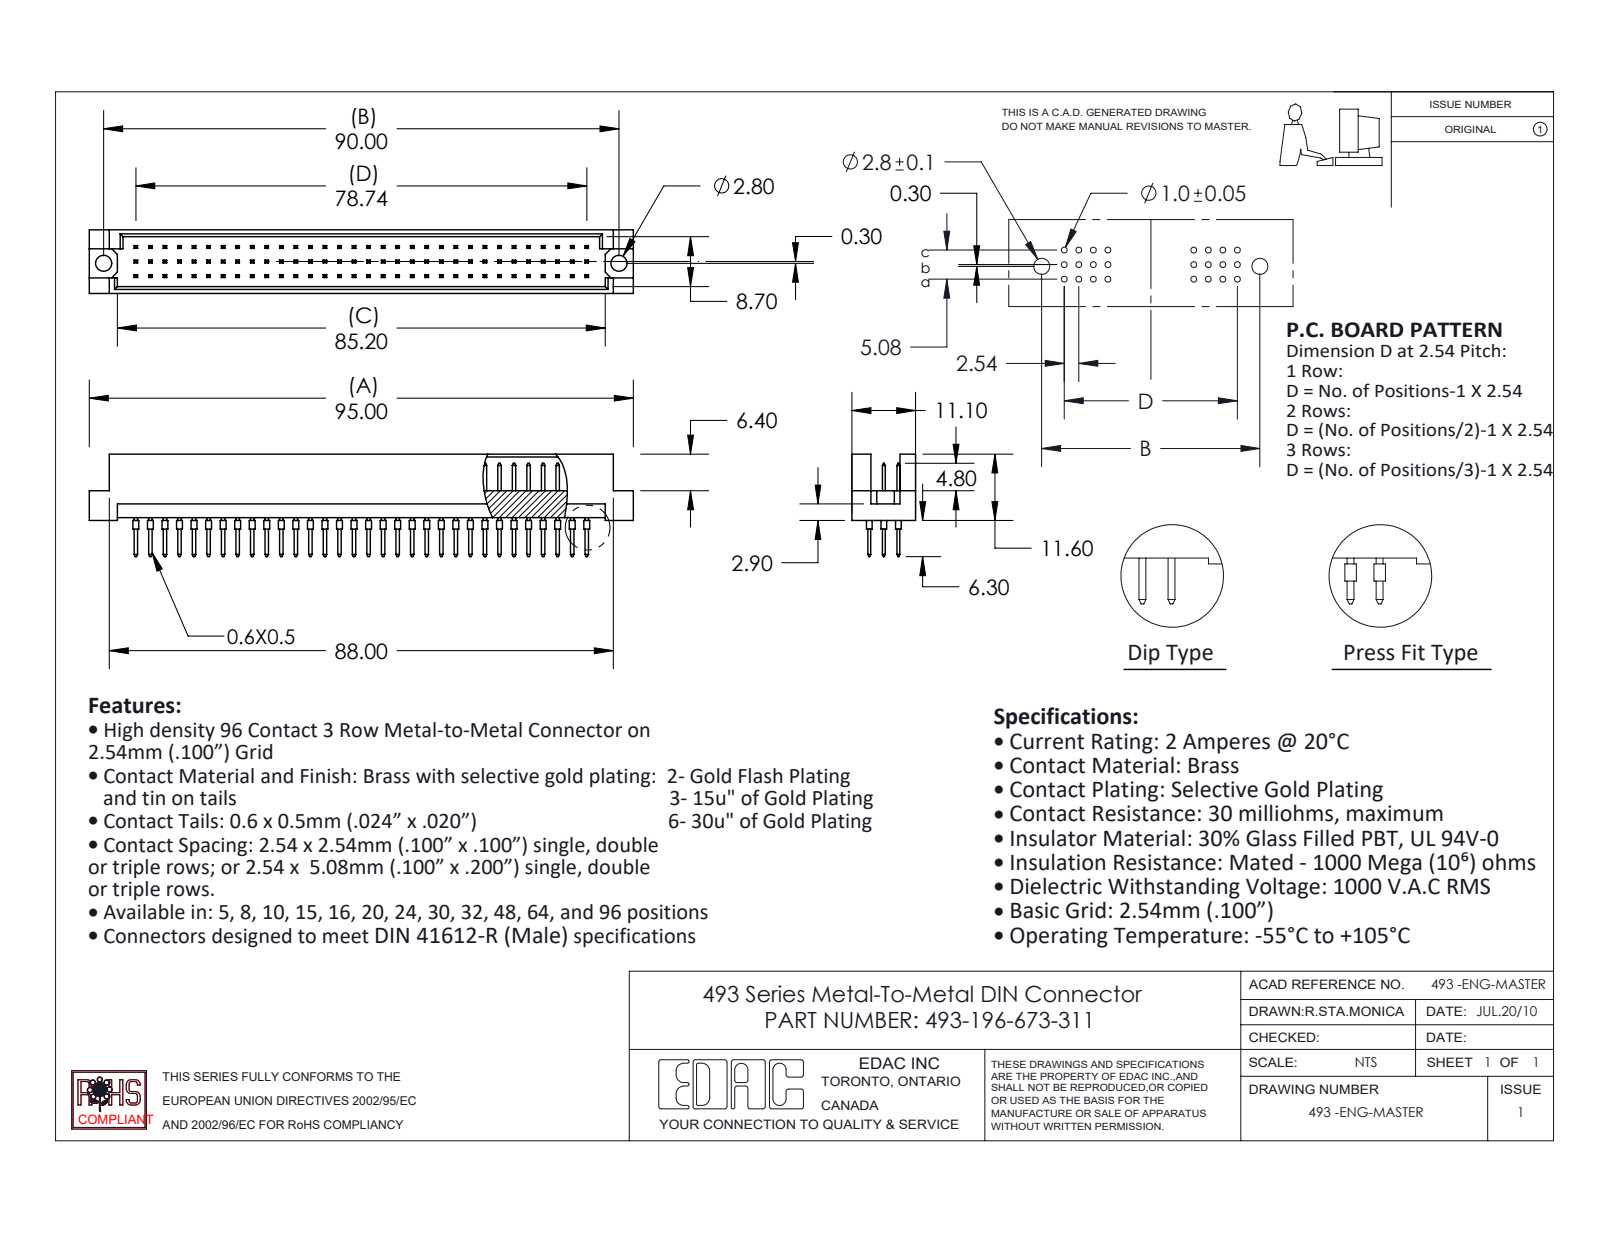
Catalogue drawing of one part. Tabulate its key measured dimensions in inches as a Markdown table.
| quantity | value |
| --- | --- |
| part name | 493 Part_96; 493-290_73; 493-196-673-311 |
| STEP written by | SolidWorks 2020 (CONFIG_CONTROL_DESIGN) |
| units | inches |
| bodies | 97 solids, 2548 faces (2352 planar, 196 cylindrical, 0 other) |
| overall size | 3.74 × 0.705 × 0.437 |
| volume | 0.378 in³ |
| surface area | 15.67 in² |
| round holes (diameter × count) | 0.11 × 2 |
| round bosses / shafts (diameter × count) | 0.039 × 96 |
| main face-to-face distances | 0.1, 0.047, 0.39, 0.02, 0.2, 0.437, 0.343, 0.109, 0.128, 0.209 |
| hole center spacings | 3.543 |
